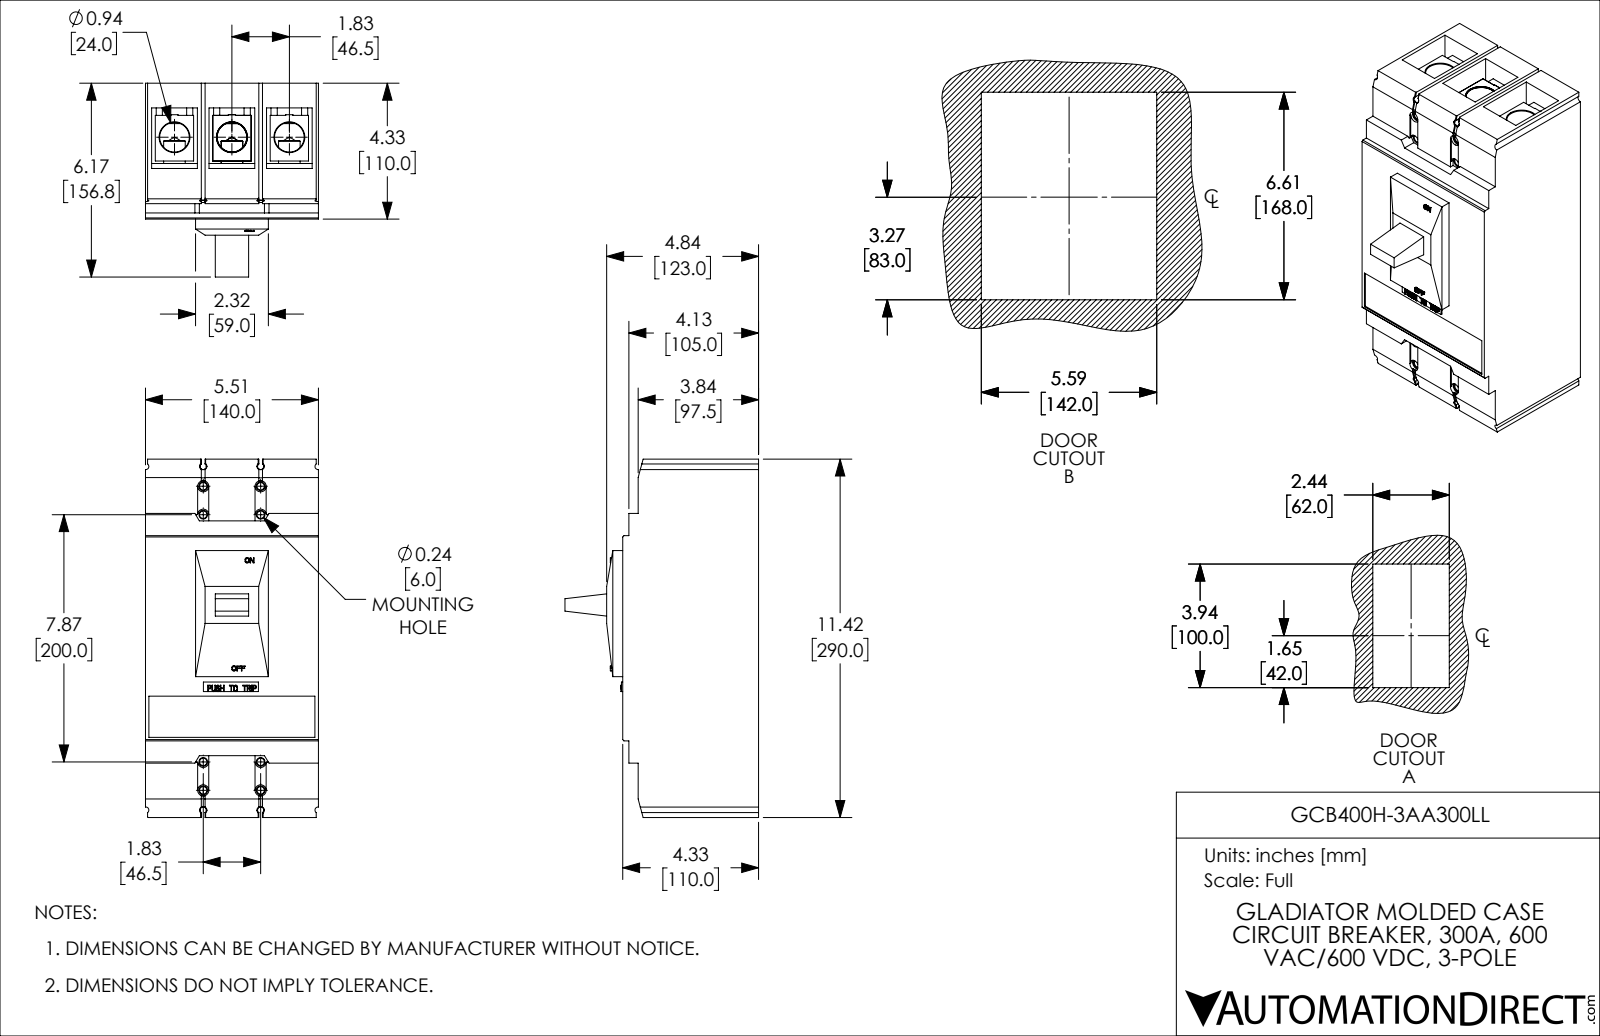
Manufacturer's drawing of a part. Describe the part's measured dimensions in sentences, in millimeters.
The part is named "GCB400H-3AA300LL". Its 3-D file was written by "SolidWorks 2021 (CONFIG_CONTROL_DESIGN)". It is 26 solids with 1319 faces: 935 planar, 200 cylindrical and 184 other. Overall it measures 290 by 156.8 by 140 millimeters. Its volume is 4 028 000 cubic millimeters and its surface area 339 200 square millimeters. Round holes: 8 of diameter 6, 6 of diameter 10.5, 6 of diameter 15.1, 6 of diameter 17.5, 4 of diameter 5, 4 of diameter 9, 3 of diameter 24. Round bosses or shafts: 6 of diameter 14.6, 6 of diameter 10, 1 of diameter 19.1. Partial cylindrical surfaces (rounded edges, fillets, slot ends): 28 of radius 2.5, 8 of radius 1, 4 of radius 4.5. The main face-to-face distances are 46.5, 140, 12.5, 37, 3, 34, 45, 43.5, 49.5, 5. The hole center spacings are 46.5, 24.6, 27.7, 33.4, 216.3, 239.1, 255.1, 16.
